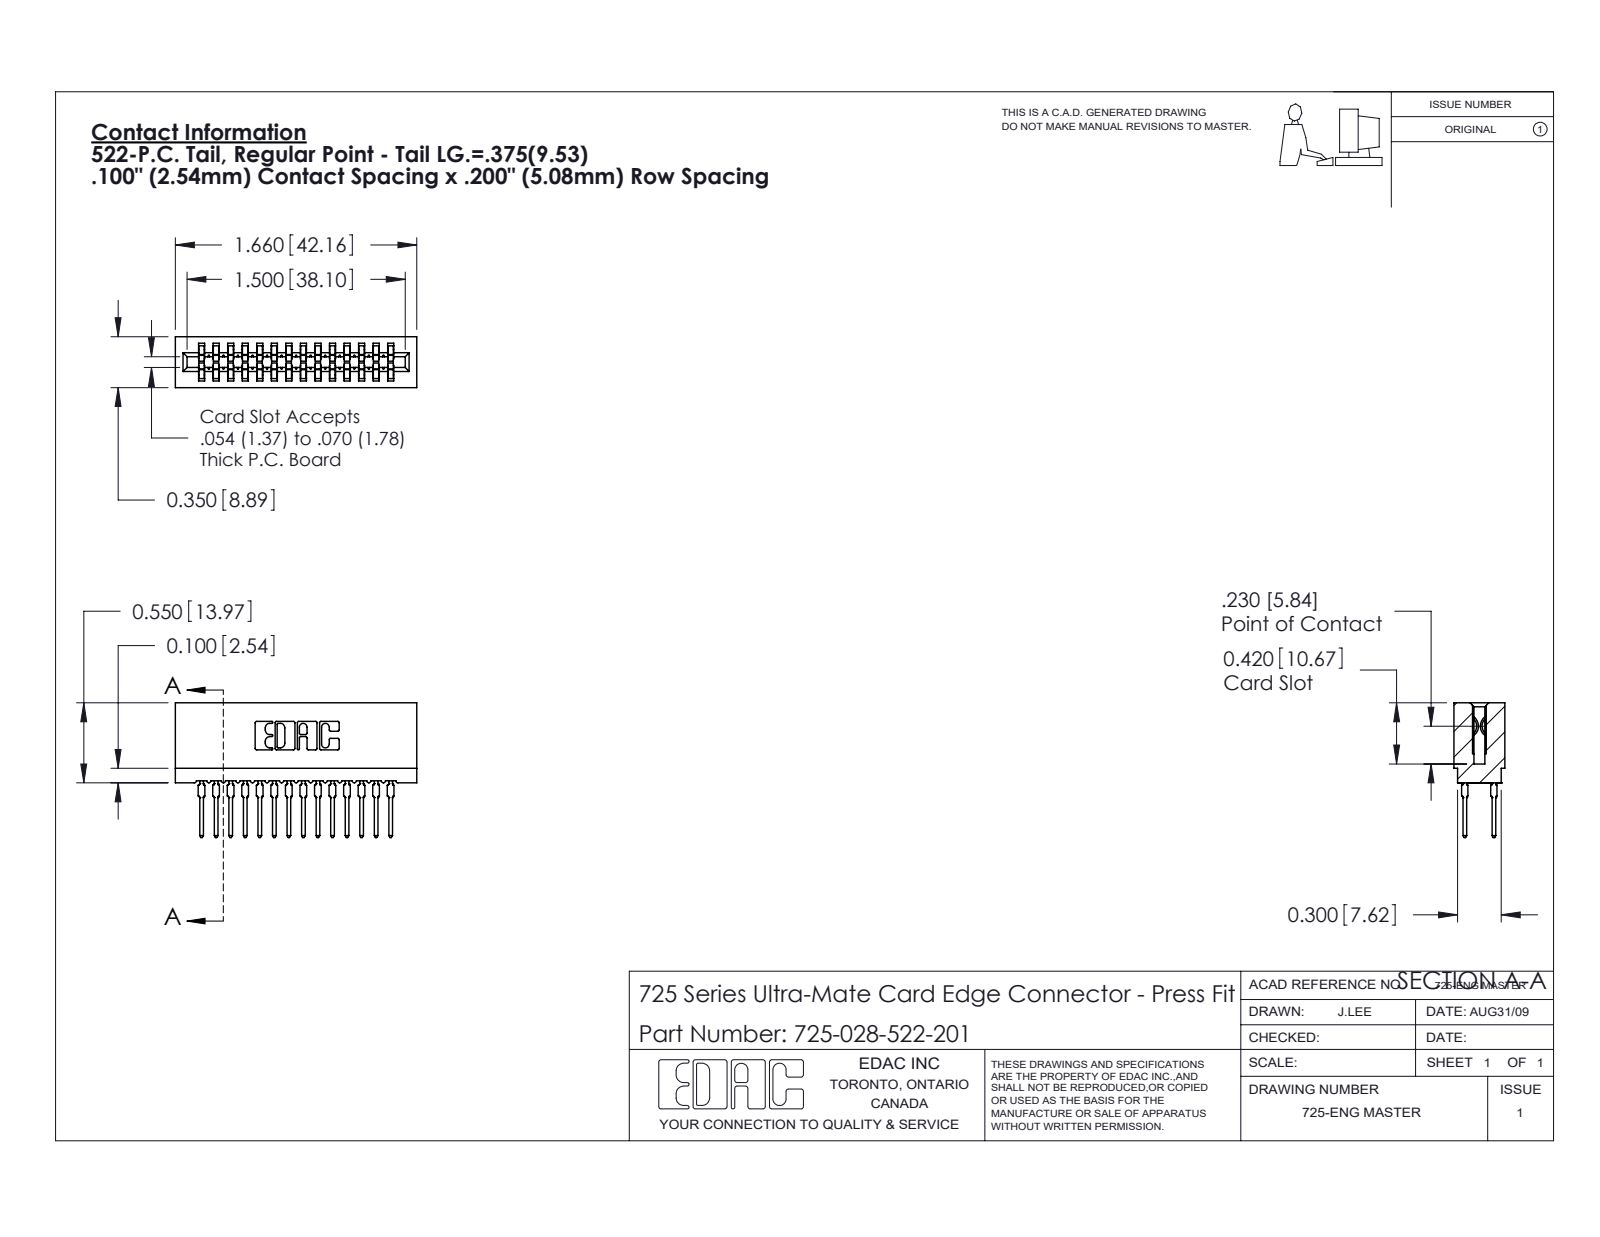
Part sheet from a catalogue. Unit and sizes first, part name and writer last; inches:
Units: inches
Overall size (bounding box): 1.66 × 0.926 × 0.35
Partial cylindrical surfaces — rounded edges, fillets, slot ends (radius × count): R0.021 ×56, R0.015 ×28, R0.01 ×22, R0.005 ×8, R0.011 ×8, R0.007 ×6, R0.031 ×6, R0.026 ×3
Main face-to-face distances: 0.2, 0.1, 0.3, 0.6, 0.4, 0.5, 0.7, 0.063, 0.287, 0.35
Volume: 0.214 in³ · Surface area: 10.74 in²
Bodies: 29 solids, 2601 faces (1343 planar, 530 cylindrical, 728 other)
Part name (STEP PRODUCT): 725 Part_Insulator Option - 01; 745-292-001_522; 725-028-522-201
STEP written by: SolidWorks 2020 (CONFIG_CONTROL_DESIGN)
